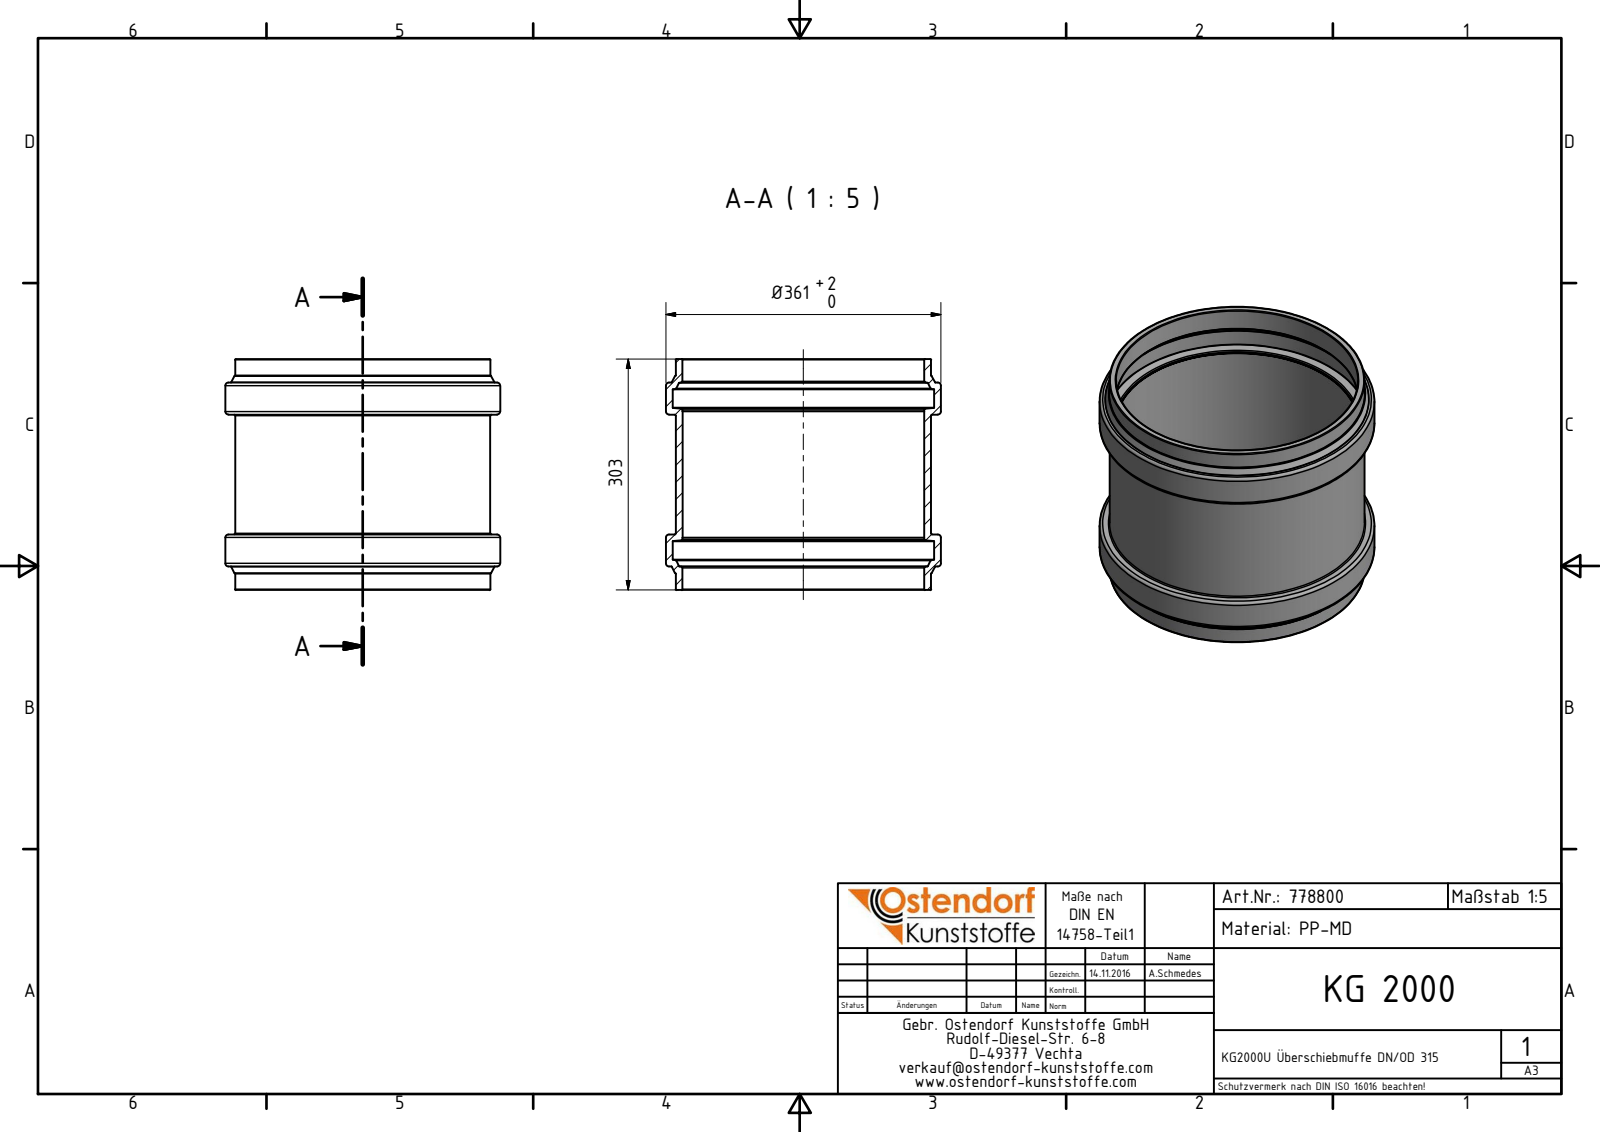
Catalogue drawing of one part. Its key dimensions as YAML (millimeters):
part_name: "778800 KG2000U Überschiebmuffe DN_OD 315"
step_written_by: "Autodesk Inventor 2016 (AUTOMOTIVE_DESIGN)"
units: millimeters
bodies: {solids: 1, faces: 58, planar: 8, cylindrical: 12, other: 38}
overall_size: [360.8, 360.8, 303]
volume: 3168000
surface_area: 727711
round_holes:
  - {diameter: 317.1, count: 1}
  - {diameter: 317.5, count: 1}
  - {diameter: 343.2, count: 1}
round_bosses_or_shafts:
  - {diameter: 360.8, count: 1}
  - {diameter: 335.1, count: 1}
  - {diameter: 334.7, count: 1}
face_to_face_distances: [72.9, 230.1, 157.2, 303, 30.9, 272.1, 42, 199.2, 241.2, 68.57]
